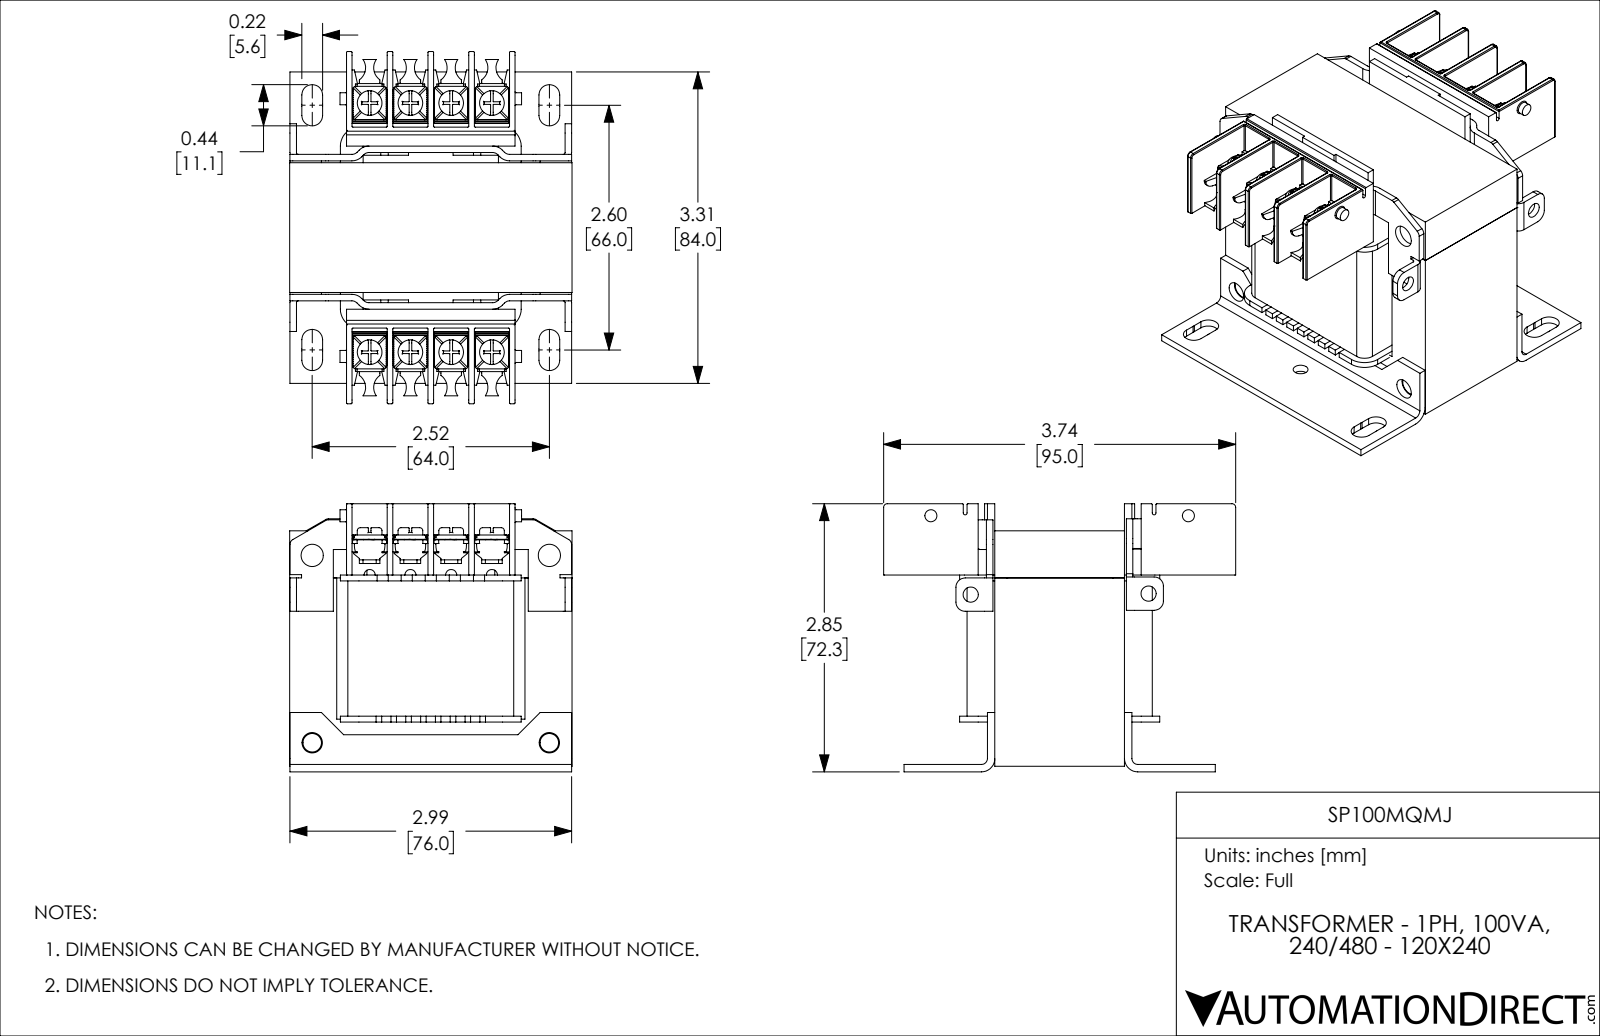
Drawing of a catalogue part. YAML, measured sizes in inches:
part_name: "SP100MQMJ"
step_written_by: "SolidWorks 2018 (AUTOMOTIVE_DESIGN)"
units: inches
bodies: {solids: 41, faces: 3158, planar: 1936, cylindrical: 931, other: 291}
overall_size: [3.74, 3, 2.847]
volume: 13.95
surface_area: 138
round_holes:
  - {diameter: 0.157, count: 10}
  - {diameter: 0.105, count: 8}
  - {diameter: 0.138, count: 8}
  - {diameter: 0.236, count: 4}
  - {diameter: 0.161, count: 2}
  - {diameter: 0.197, count: 2}
  - {diameter: 0.217, count: 2}
round_bosses_or_shafts:
  - {diameter: 0.262, count: 8}
  - {diameter: 0.24, count: 8}
  - {diameter: 0.168, count: 8}
  - {diameter: 0.11, count: 8}
  - {diameter: 0.128, count: 3}
partial_cylinders:
  - {radius: 0.005, count: 52}
  - {radius: 0.01, count: 52}
  - {radius: 0.012, count: 40}
  - {radius: 0.029, count: 32}
  - {radius: 0.059, count: 22}
  - {radius: 0.157, count: 16}
  - {radius: 0.035, count: 12}
  - {radius: 0.079, count: 10}
face_to_face_distances: [0.5, 2, 0.059, 2.5, 1.378, 0.433, 0.079, 0.02, 0.118, 1]
hole_center_spacings: [0.433, 0.866, 2.671, 1.299, 2.636, 2.774, 2.661, 2.681]
